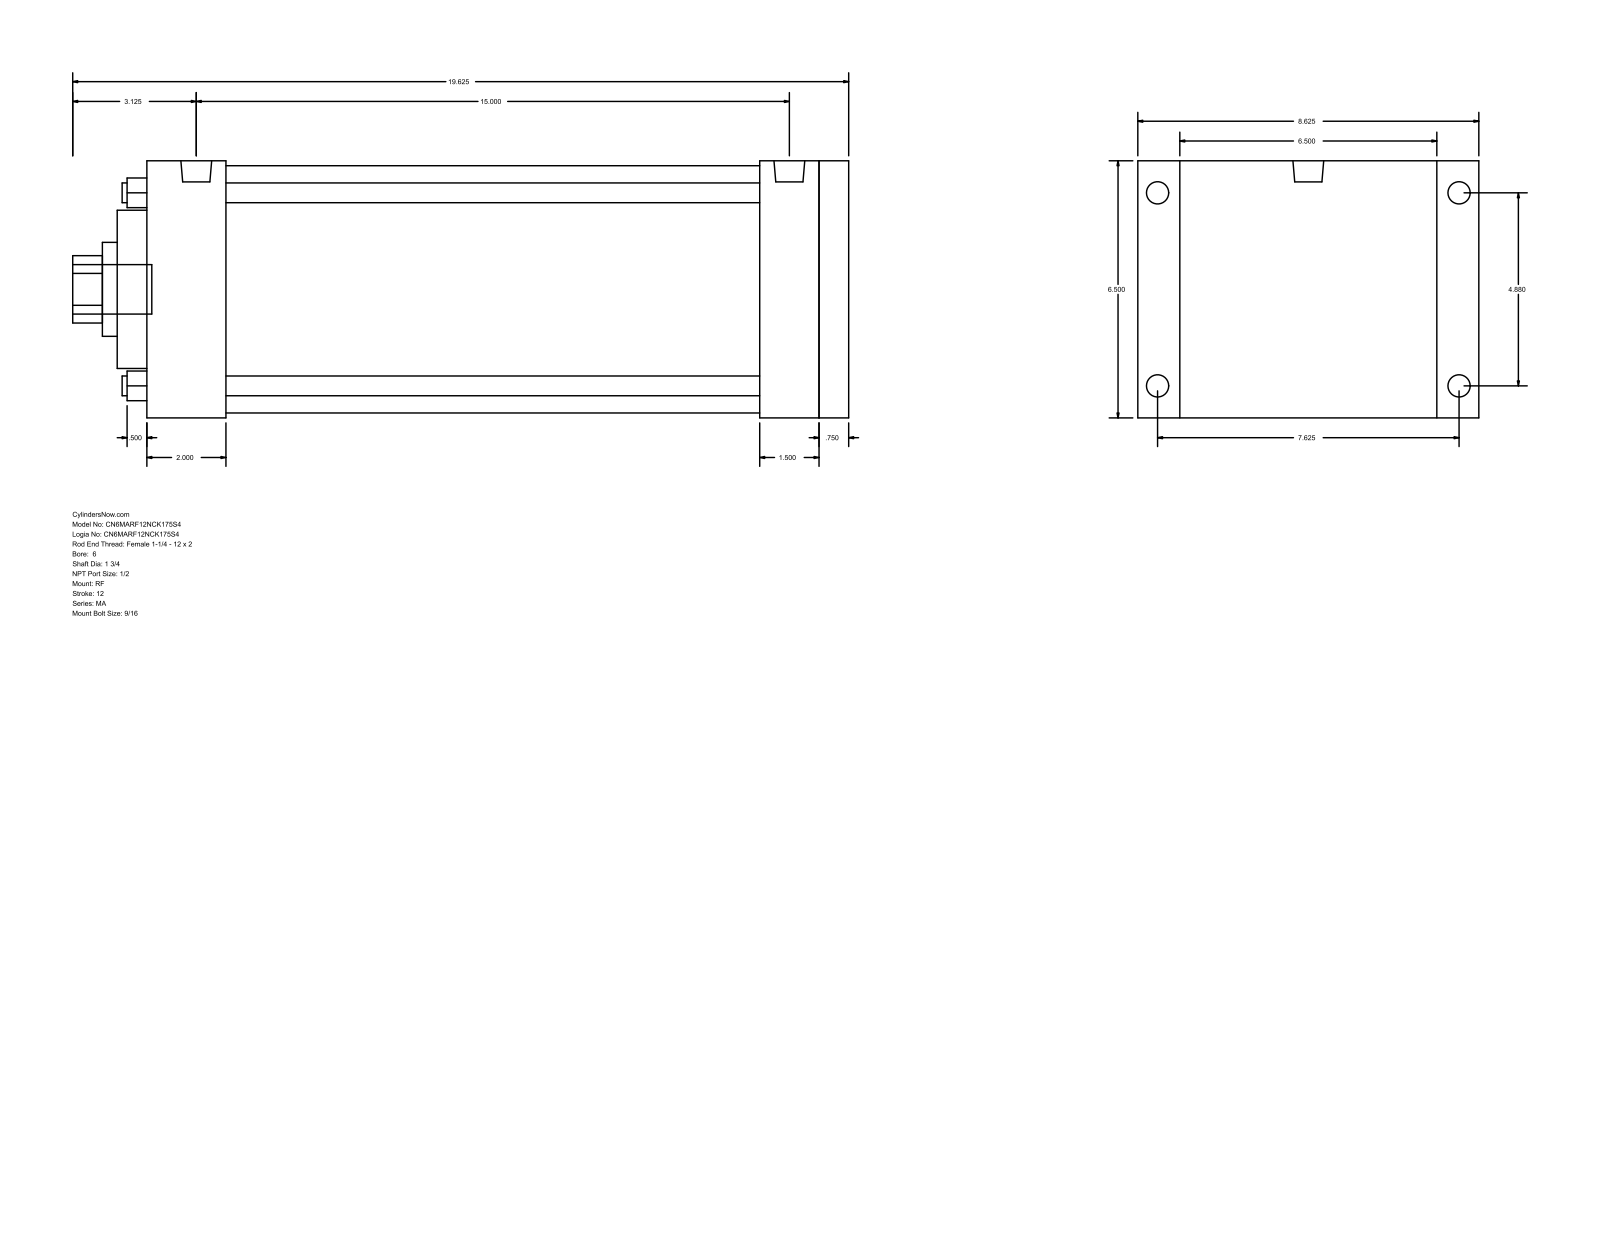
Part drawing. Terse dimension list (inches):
name: MA_RF__0600_1.75
written by: GSSL Pune (CONFIG_CONTROL_DESIGN)
unit: in
bodies: 0 solids, 94 faces (65 planar, 29 cylindrical, 0 other)
size: 19.625 × 8.625 × 6.5
holes: 4× ⌀0.5, 1× ⌀1.75, 1× ⌀2.375, 1× ⌀4, 1× ⌀6.25
bosses: 4× ⌀0.687, 4× ⌀0.563, 2× ⌀0.778, 1× ⌀1.25
rounds: 1× R0.852
face distances: 6.5, 17.75, 0.75, 17, 2, 15, 15.75, 15.5, 13.5, 1.5
hole spacings: 3.451, 4.88, 6.902
